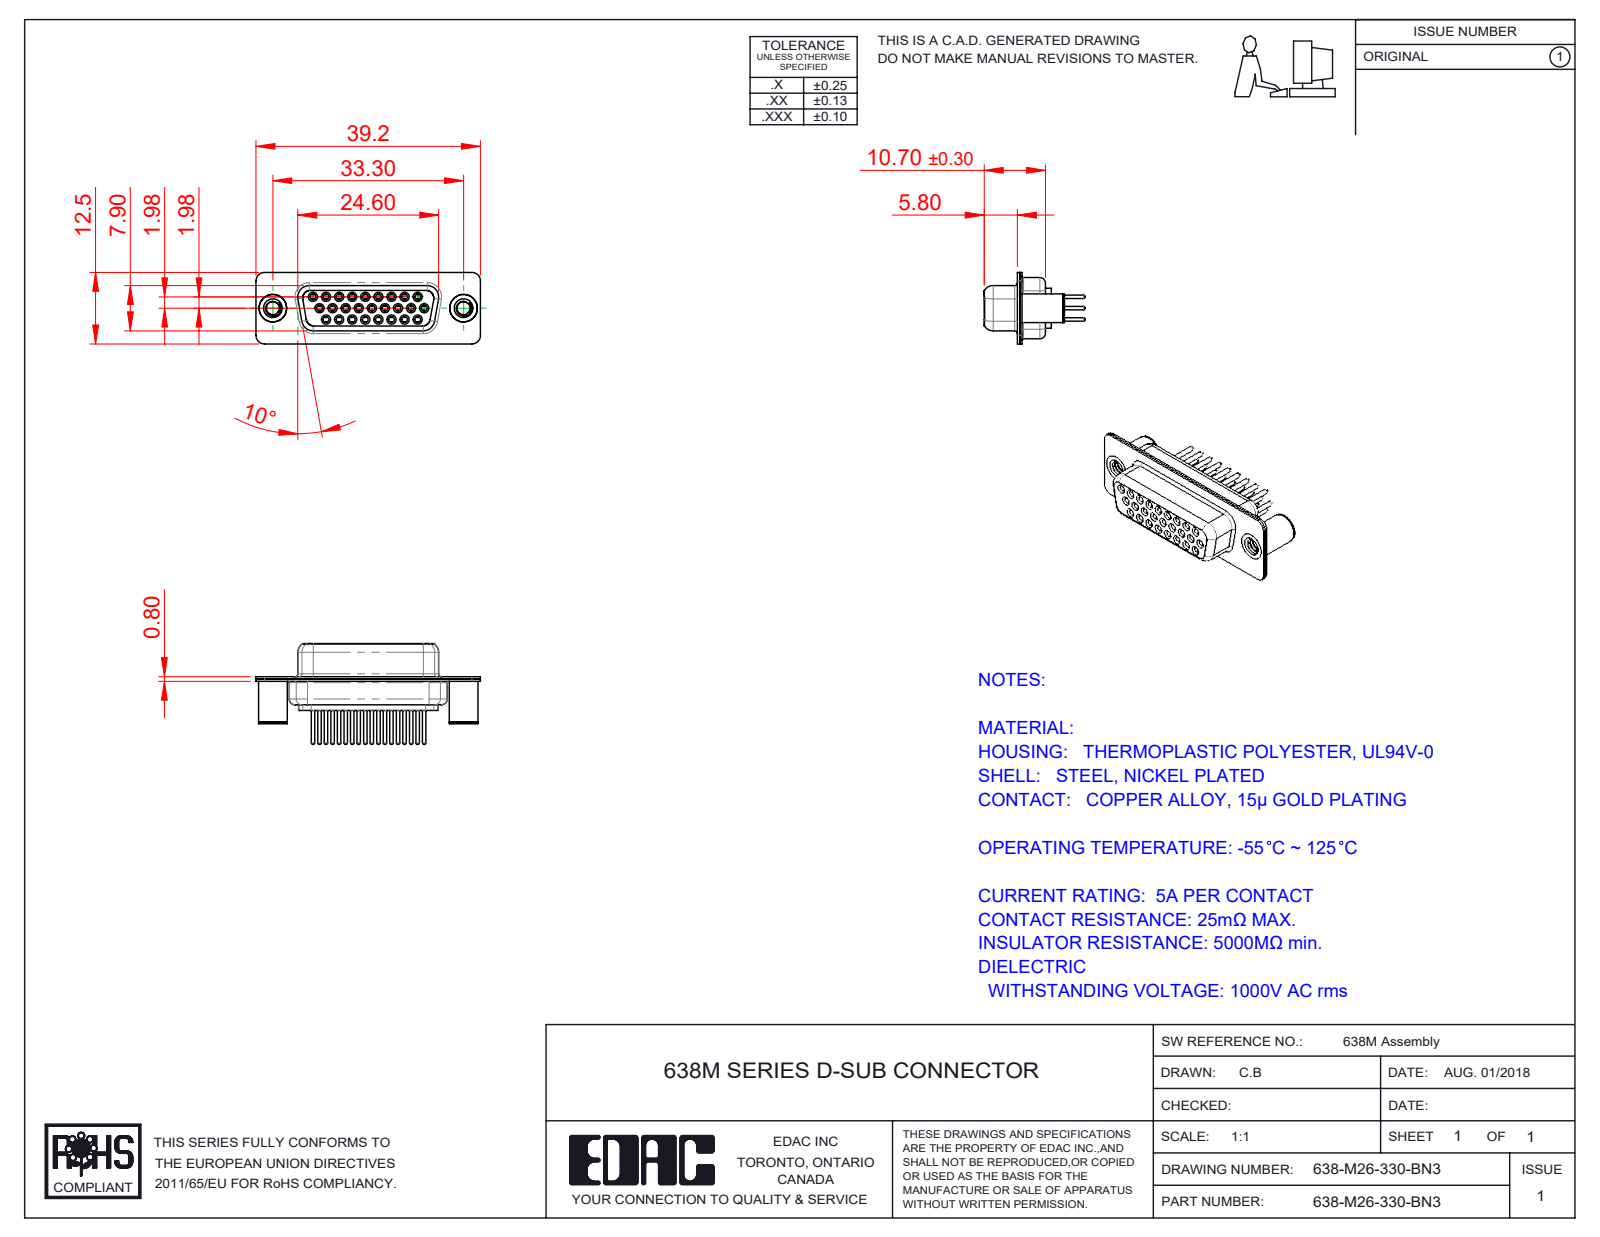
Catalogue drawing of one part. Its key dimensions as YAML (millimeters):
part_name: "638M Shell Front_26 Contacts; 638M Contact Row 3_30; 638M Housing_26 Contacts; 638M Shell Rear_26 Contacts (+4 more)"
step_written_by: "SolidWorks 2020 (CONFIG_CONTROL_DESIGN)"
units: millimeters
bodies: {solids: 31, faces: 1743, planar: 457, cylindrical: 655, other: 631}
overall_size: [39.2, 17.6, 12.5]
volume: 2476
surface_area: 8120
round_holes:
  - {diameter: 1, count: 26}
  - {diameter: 1.1, count: 26}
  - {diameter: 1.7, count: 26}
  - {diameter: 1.8, count: 26}
  - {diameter: 2, count: 26}
  - {diameter: 2.26, count: 2}
  - {diameter: 3.26, count: 2}
  - {diameter: 4, count: 2}
  - {diameter: 4.8, count: 2}
round_bosses_or_shafts:
  - {diameter: 2.2, count: 26}
  - {diameter: 1.6, count: 26}
  - {diameter: 1.5, count: 26}
  - {diameter: 0.6, count: 26}
  - {diameter: 5, count: 2}
  - {diameter: 4.9, count: 2}
partial_cylinders:
  - {radius: 1.5, count: 16}
  - {radius: 2, count: 12}
  - {radius: 1.35, count: 8}
  - {radius: 1.6, count: 8}
  - {radius: 0.25, count: 4}
  - {radius: 0.5, count: 4}
  - {radius: 0.6, count: 4}
  - {radius: 0.65, count: 4}
face_to_face_distances: [0.4, 1.4, 0.45, 8.45, 8.9, 1.8, 1, 6.2, 7.05, 1.85]
hole_center_spacings: [3.96, 2.28, 4.57, 6.05, 2.29, 8.24, 6.86, 6.04]
